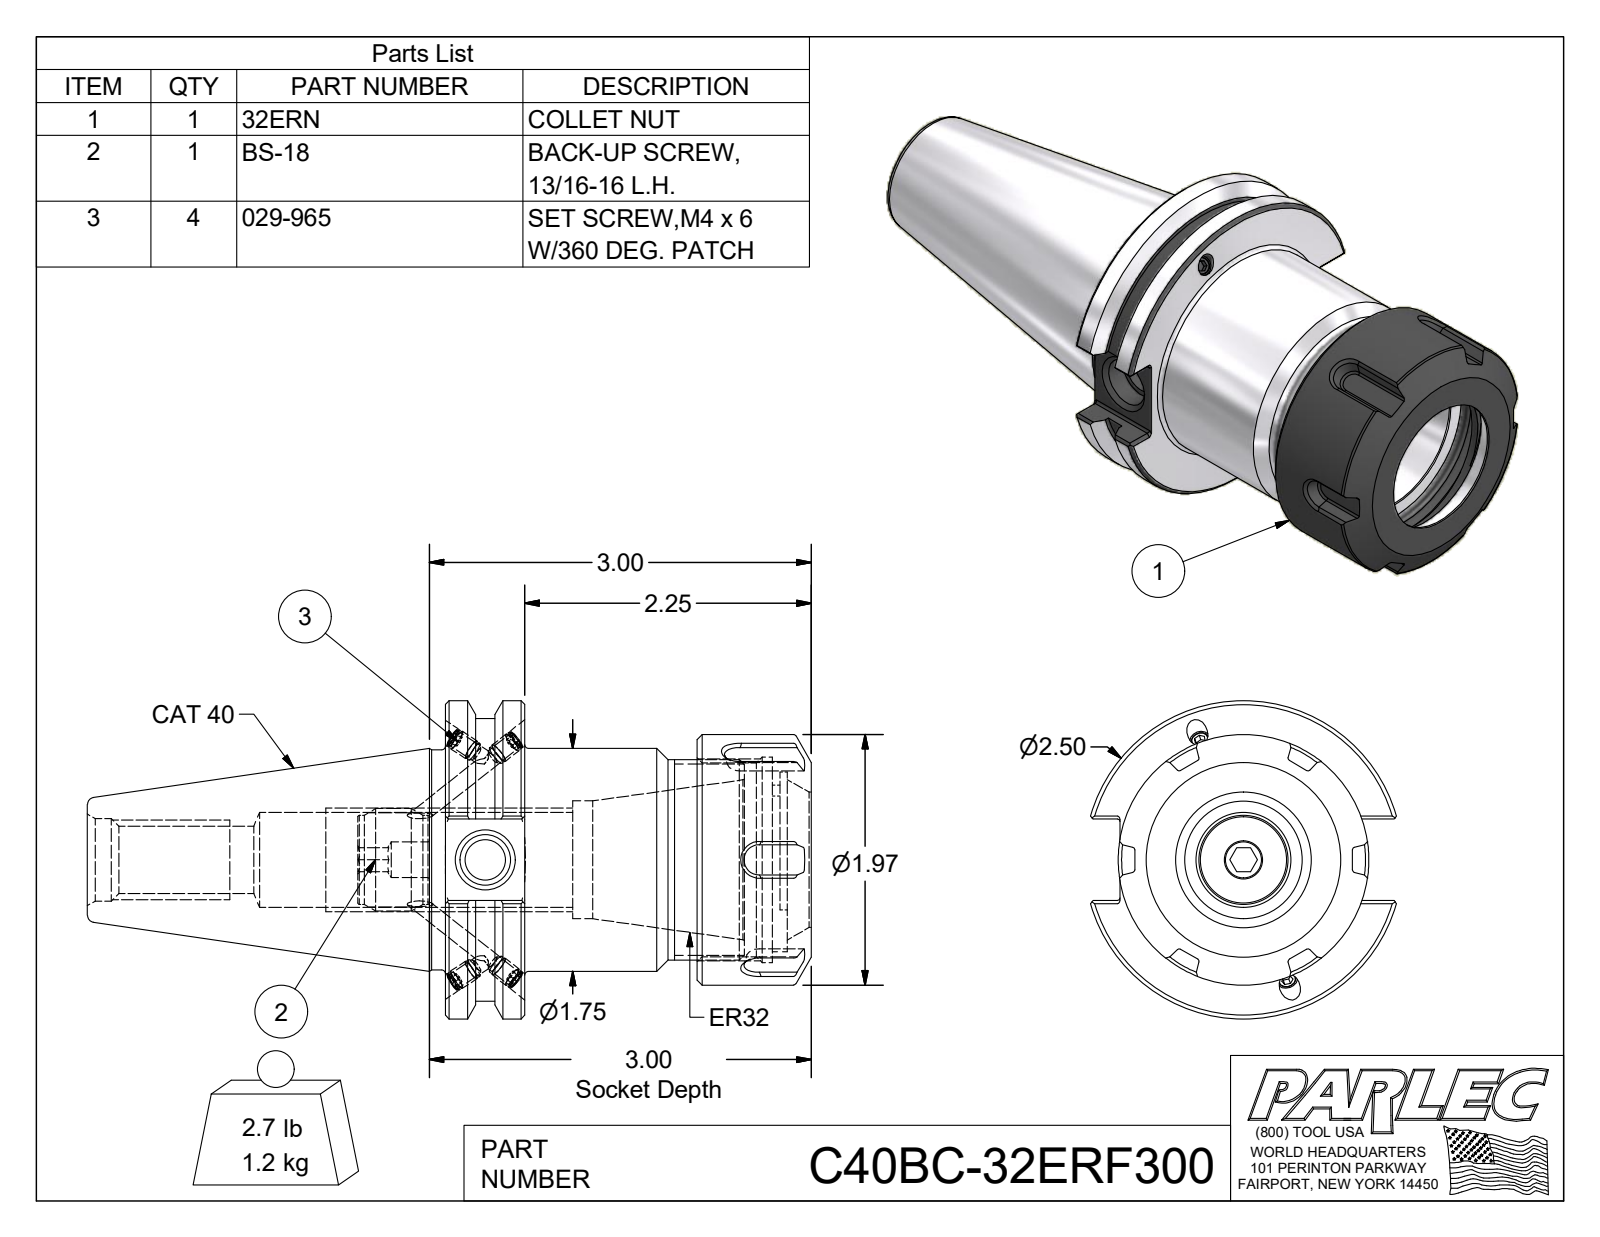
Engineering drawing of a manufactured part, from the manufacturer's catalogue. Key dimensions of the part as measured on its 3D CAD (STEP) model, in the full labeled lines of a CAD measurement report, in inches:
Part name (STEP PRODUCT): C40BCB-32ER3-1; 029-965; 32ERN; BS-18 (+1 more)
STEP written by: Autodesk Inventor 2016 (AUTOMOTIVE_DESIGN)
Units: inches
Bodies: 7 solids, 263 faces (119 planar, 70 cylindrical, 74 other)
Overall size (bounding box): 5.687 × 2.5 × 2.404
Volume: 9.433 in³ · Surface area: 64.36 in²
Round holes (diameter × count): ⌀0.13 ×4, ⌀0.161 ×4, ⌀0.28 ×1, ⌀0.315 ×1, ⌀0.399 ×1, ⌀0.527 ×1, ⌀0.648 ×1, ⌀0.745 ×1, ⌀0.925 ×1, ⌀1.063 ×1, ⌀1.3 ×1, ⌀1.522 ×1
Round bosses / shafts (diameter × count): ⌀0.165 ×4, ⌀0.157 ×4, ⌀2.5 ×1, ⌀2.219 ×1, ⌀1.969 ×1, ⌀1.75 ×1, ⌀1.73 ×1, ⌀1.575 ×1
Partial cylindrical surfaces — rounded edges, fillets, slot ends (radius × count): R0.02 ×24, R0.587 ×1, R0.689 ×1
Main face-to-face distances: 0.625, 2.875, 2.25, 1.978, 1.353, 0.897, 2.569, 1.944, 0.591, 0.306
Hole centre spacings: 0.073
